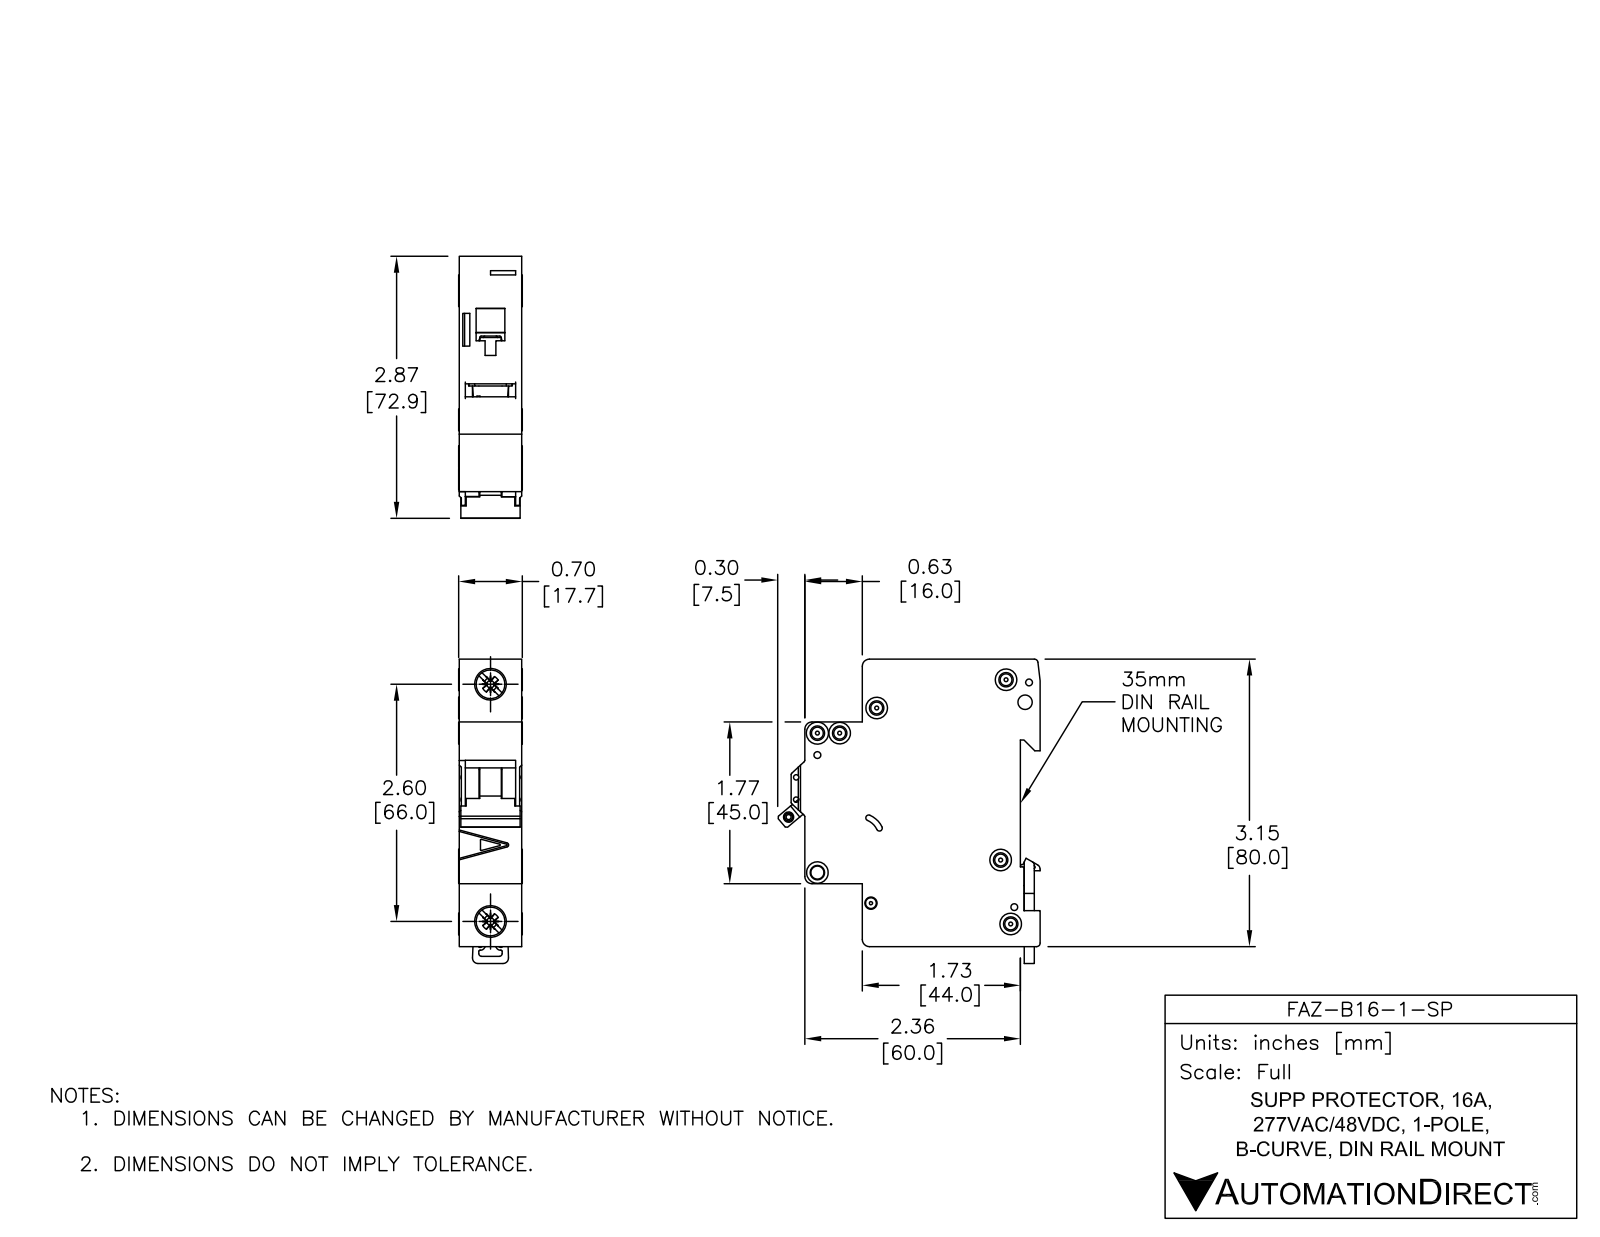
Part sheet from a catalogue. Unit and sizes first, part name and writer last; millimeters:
Units: millimetres
Overall size (bounding box): 84.78 × 73.04 × 17.7
Round holes (diameter × count): ⌀3.6 ×6, ⌀1.9 ×3, ⌀1.09 ×2, ⌀1.5 ×2, ⌀4 ×2, ⌀7.15 ×2, ⌀2.15 ×1, ⌀2.2 ×1, ⌀2.55 ×1, ⌀3.3 ×1, ⌀3.4 ×1
Round bosses / shafts (diameter × count): ⌀6 ×4, ⌀8.2 ×2, ⌀2.5 ×1
Partial cylindrical surfaces — rounded edges, fillets, slot ends (radius × count): R0.25 ×30, R0.5 ×13, R2 ×8, R0.2 ×5, R1 ×4, R0.8 ×2, R3 ×2, R1.5 ×1
Main face-to-face distances: 17.5, 79.48, 5.5, 49.5, 44, 65.5, 60, 16, 1.75, 15.75
Hole centre spacings: 6.2, 13.64, 4.81, 5.19, 5.61, 6.1, 6.44, 8.19
Volume: 74 935 mm³ · Surface area: 19 545 mm²
Bodies: 5 solids, 558 faces (235 planar, 202 cylindrical, 121 other)
Part name (STEP PRODUCT): FAZ-B16-1-SP
STEP written by: SolidWorks 2014 (AUTOMOTIVE_DESIGN)
